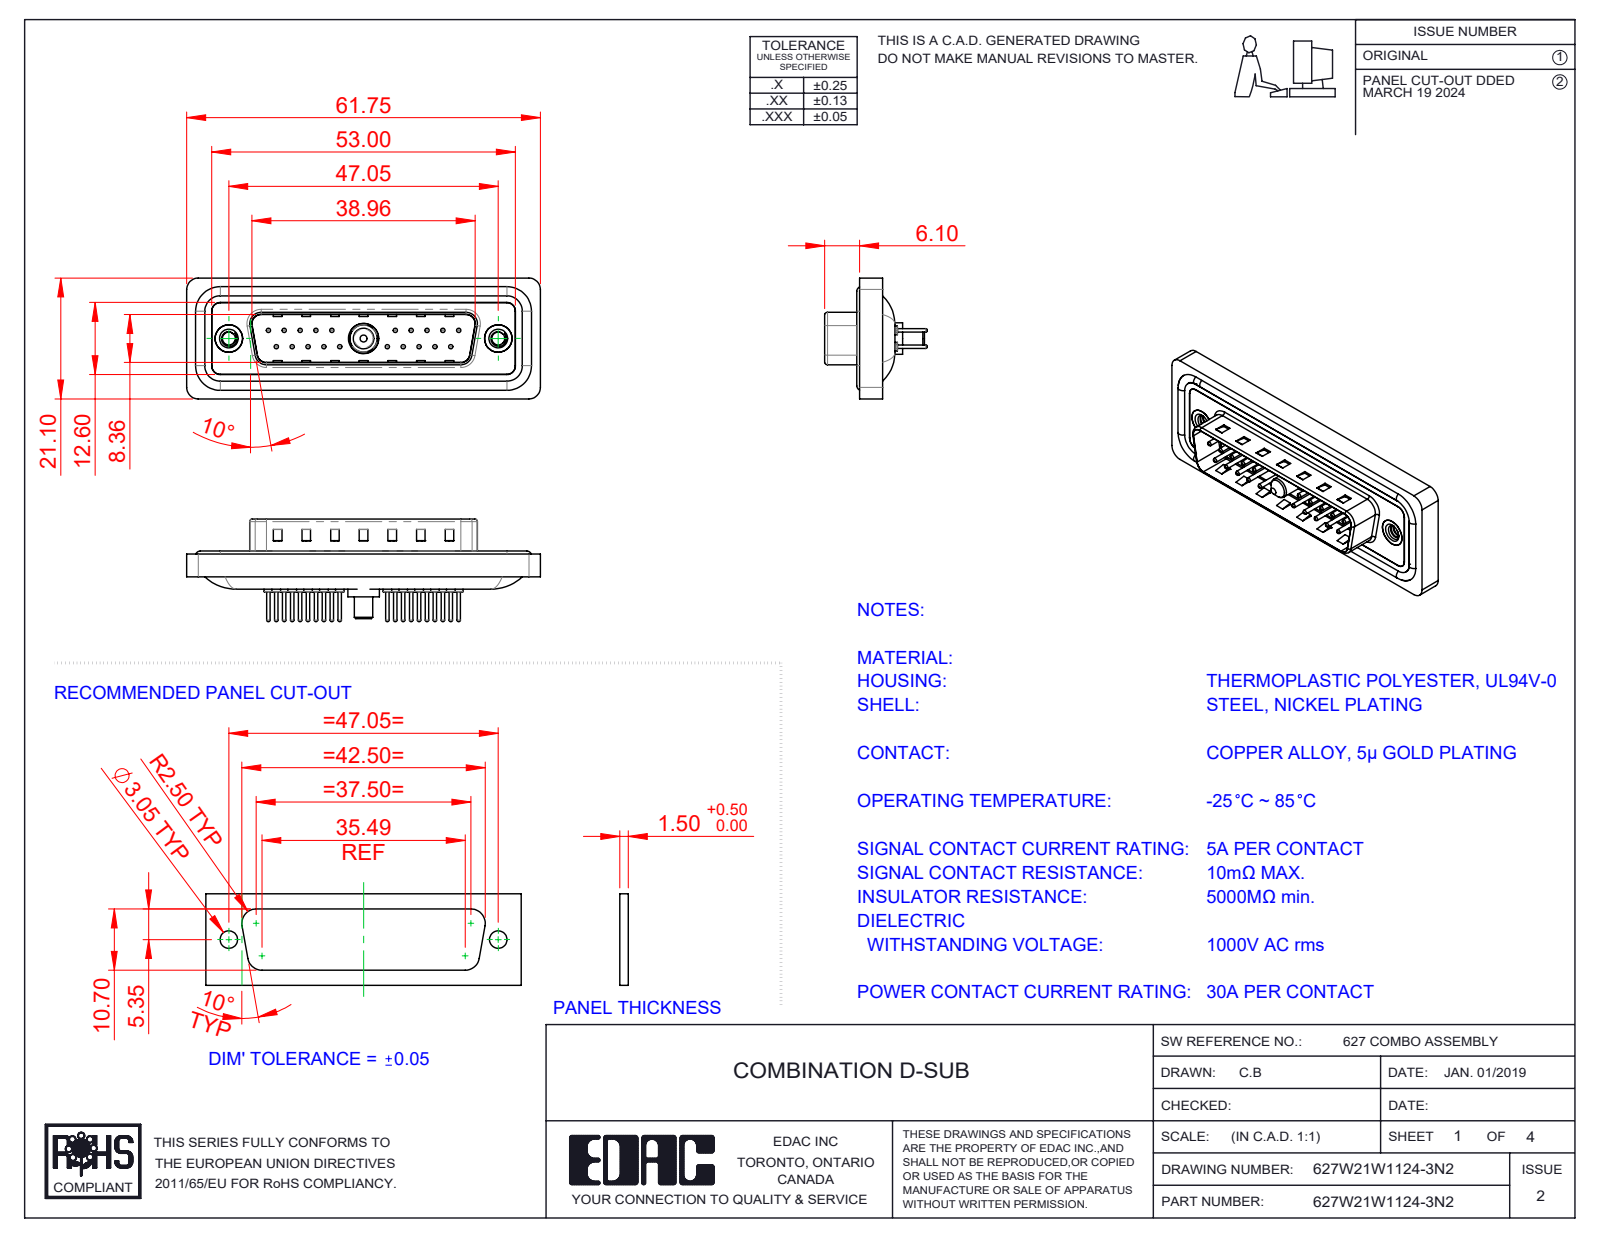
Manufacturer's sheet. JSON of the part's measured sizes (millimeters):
{"part_name": "627W21W1124-3N2; 627Combo Contact Row 1_24; 627Combo Shell Rear_25 Contacts; 627Combo Threaded Rivet_2 (+5 more)", "step_written_by": "SolidWorks 2023 (CONFIG_CONTROL_DESIGN)", "units": "millimeters", "bodies": {"solids": 29, "faces": 1262, "planar": 359, "cylindrical": 487, "other": 416}, "overall_size": [61.75, 21.1, 17.9], "volume_mm3": 7205, "surface_area_mm2": 11958, "round_holes": [[0.75, 20], [1.6, 20], [2, 20], [2.26, 2], [4, 2], [4.8, 2], [5, 2], [4.85, 1], [5.3, 1]], "round_bosses_or_shafts": [[1.5, 20], [0.6, 20], [1.6, 4], [4.9, 2], [5.5, 1], [5.2, 1], [4.75, 1], [3.75, 1]], "partial_cylinders_radius": [[1.5, 22], [2, 18], [0.5, 8], [1.6, 8], [0.25, 4], [0.6, 4], [0.65, 4], [0.9, 4]], "face_to_face_distances": [0.4, 1.5, 1.1, 1.6, 0.5, 3.1, 2.9, 4.1, 0.82, 9.58], "hole_center_spacings": [3.16, 2.77, 5.54, 8.31, 5.04, 19.39, 20.97, 22.16]}
